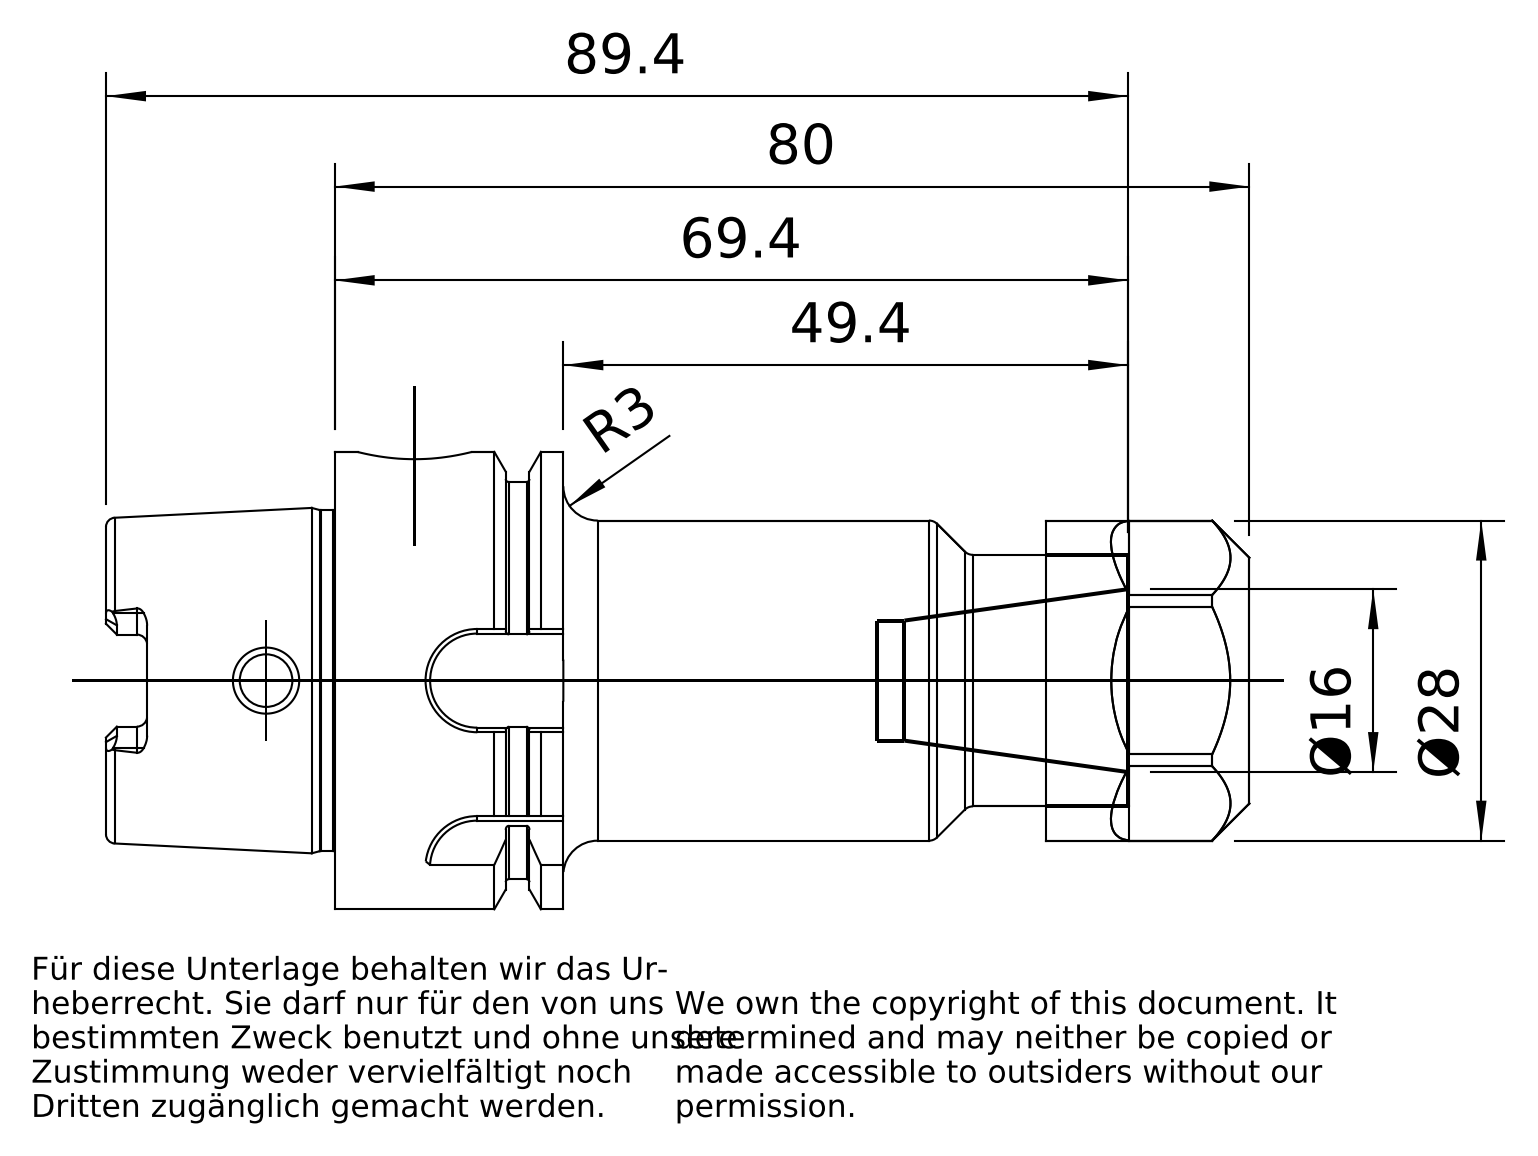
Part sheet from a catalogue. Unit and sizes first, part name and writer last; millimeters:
Units: millimetres
Overall size (bounding box): 99.9 × 40 × 40
Round holes (diameter × count): ⌀4.6 ×1, ⌀10 ×1, ⌀10.2 ×1, ⌀10.5 ×1, ⌀12 ×1, ⌀12.22 ×1, ⌀12.5 ×1, ⌀21.04 ×1, ⌀25.57 ×1
Round bosses / shafts (diameter × count): ⌀40 ×1, ⌀34.75 ×1, ⌀29.81 ×1, ⌀28 ×1, ⌀22 ×1
Partial cylindrical surfaces — rounded edges, fillets, slot ends (radius × count): R0.9 ×6, R1.88 ×4, R4.5 ×3, R4.51 ×1
Main face-to-face distances: 62.2, 25, 80, 17.8, 19.95, 42.25, 60.05, 4.4, 29.4, 7.95
Volume: 58 004 mm³ · Surface area: 16 910 mm²
Bodies: 2 solids, 217 faces (69 planar, 54 cylindrical, 94 other)
Part name (STEP PRODUCT): A40-020-16; 83-912-16; A40-020-16_ASM
STEP written by: PRO/ENGINEER BY PARAMETRIC TECHNOLOGY CORPORATION, 2010430 (CONFIG_CONTROL_DESIGN)
